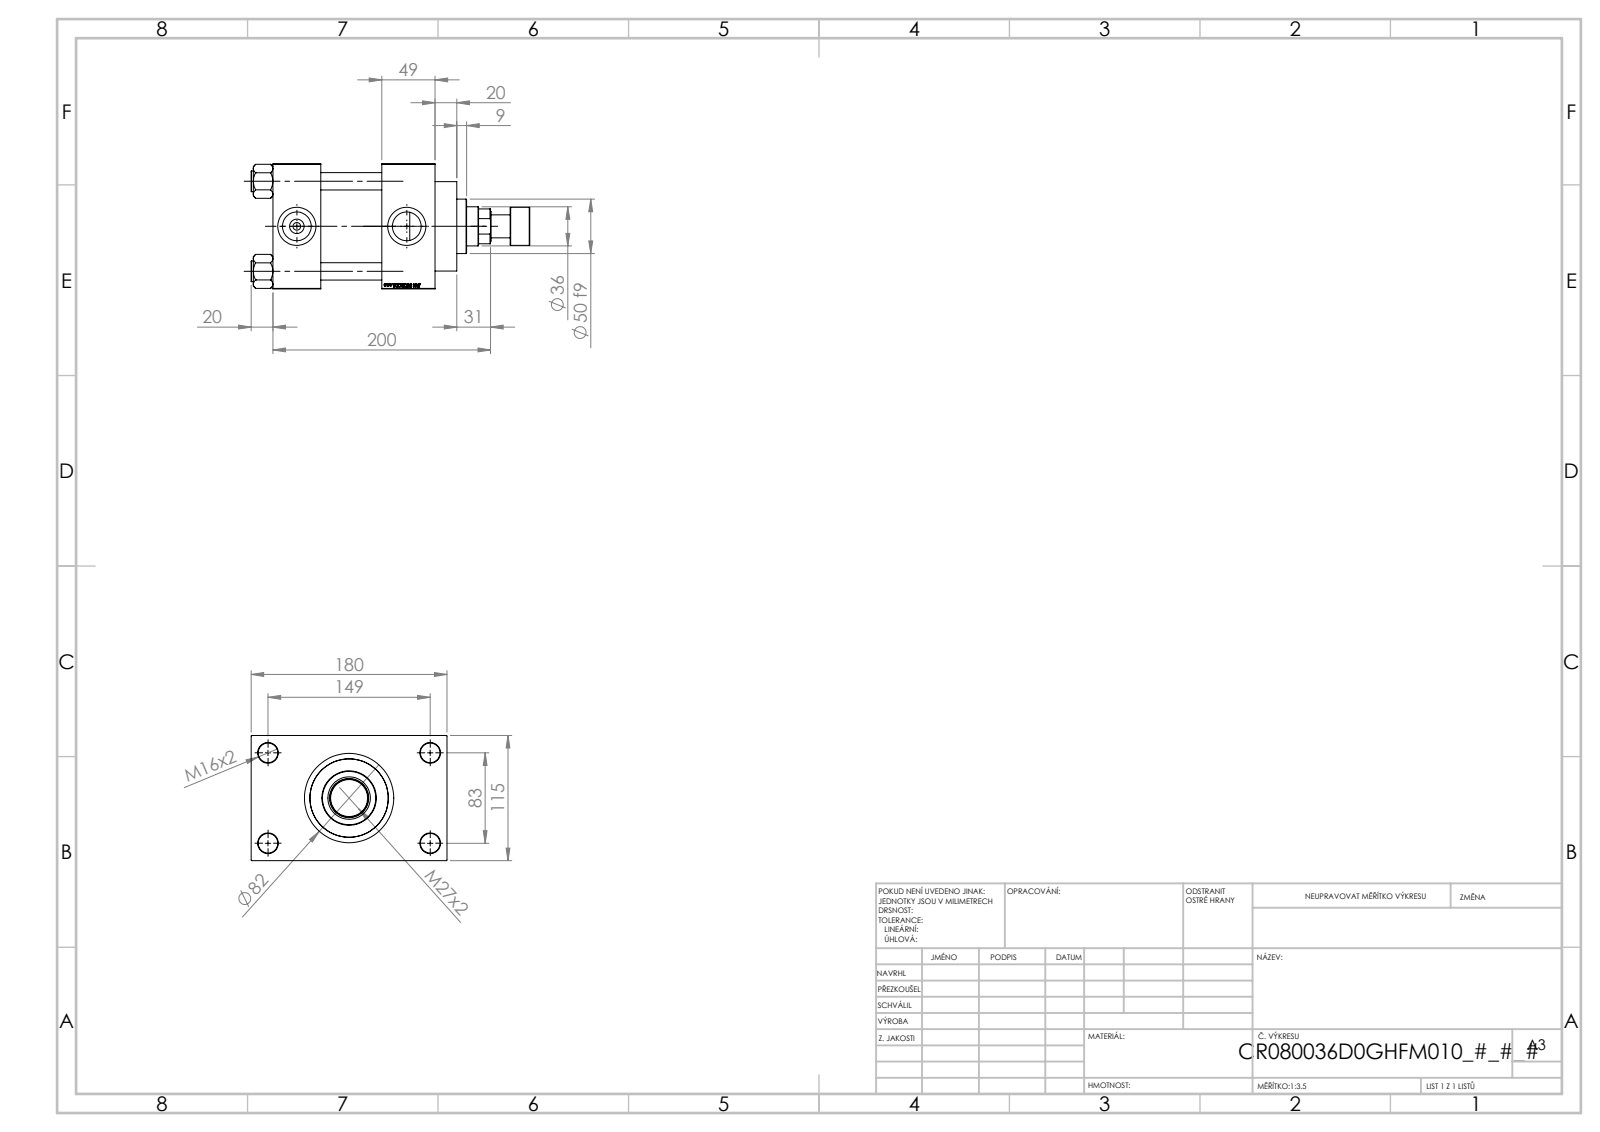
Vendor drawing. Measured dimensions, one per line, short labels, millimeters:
name: V215_VC_A; V215CR_D_TYCINKA; V215CR_ROD_END_F; V215CR_D_Body (+2 more)
written by: SolidWorks 2019 (CONFIG_CONTROL_DESIGN)
unit: mm
bodies: 12 solids, 1165 faces (549 planar, 92 cylindrical, 524 other)
size: 256 × 180 × 115
volume: 1 977 000 mm³; area: 293 805 mm²
holes: 4× ⌀16, 4× ⌀18, 2× ⌀7, 2× ⌀26.44, 2× ⌀35, 1× ⌀25.5, 1× ⌀36, 1× ⌀39, 1× ⌀61, 1× ⌀72, 1× ⌀80
bosses: 4× ⌀19, 1× ⌀86, 1× ⌀82, 1× ⌀50, 1× ⌀35, 1× ⌀21
face distances: 115, 56, 105, 49, 100, 44, 149, 32.5, 147.5, 69
hole spacings: 33.15, 58.48, 82.7, 85.28, 89.24, 115.85, 142.43, 83
